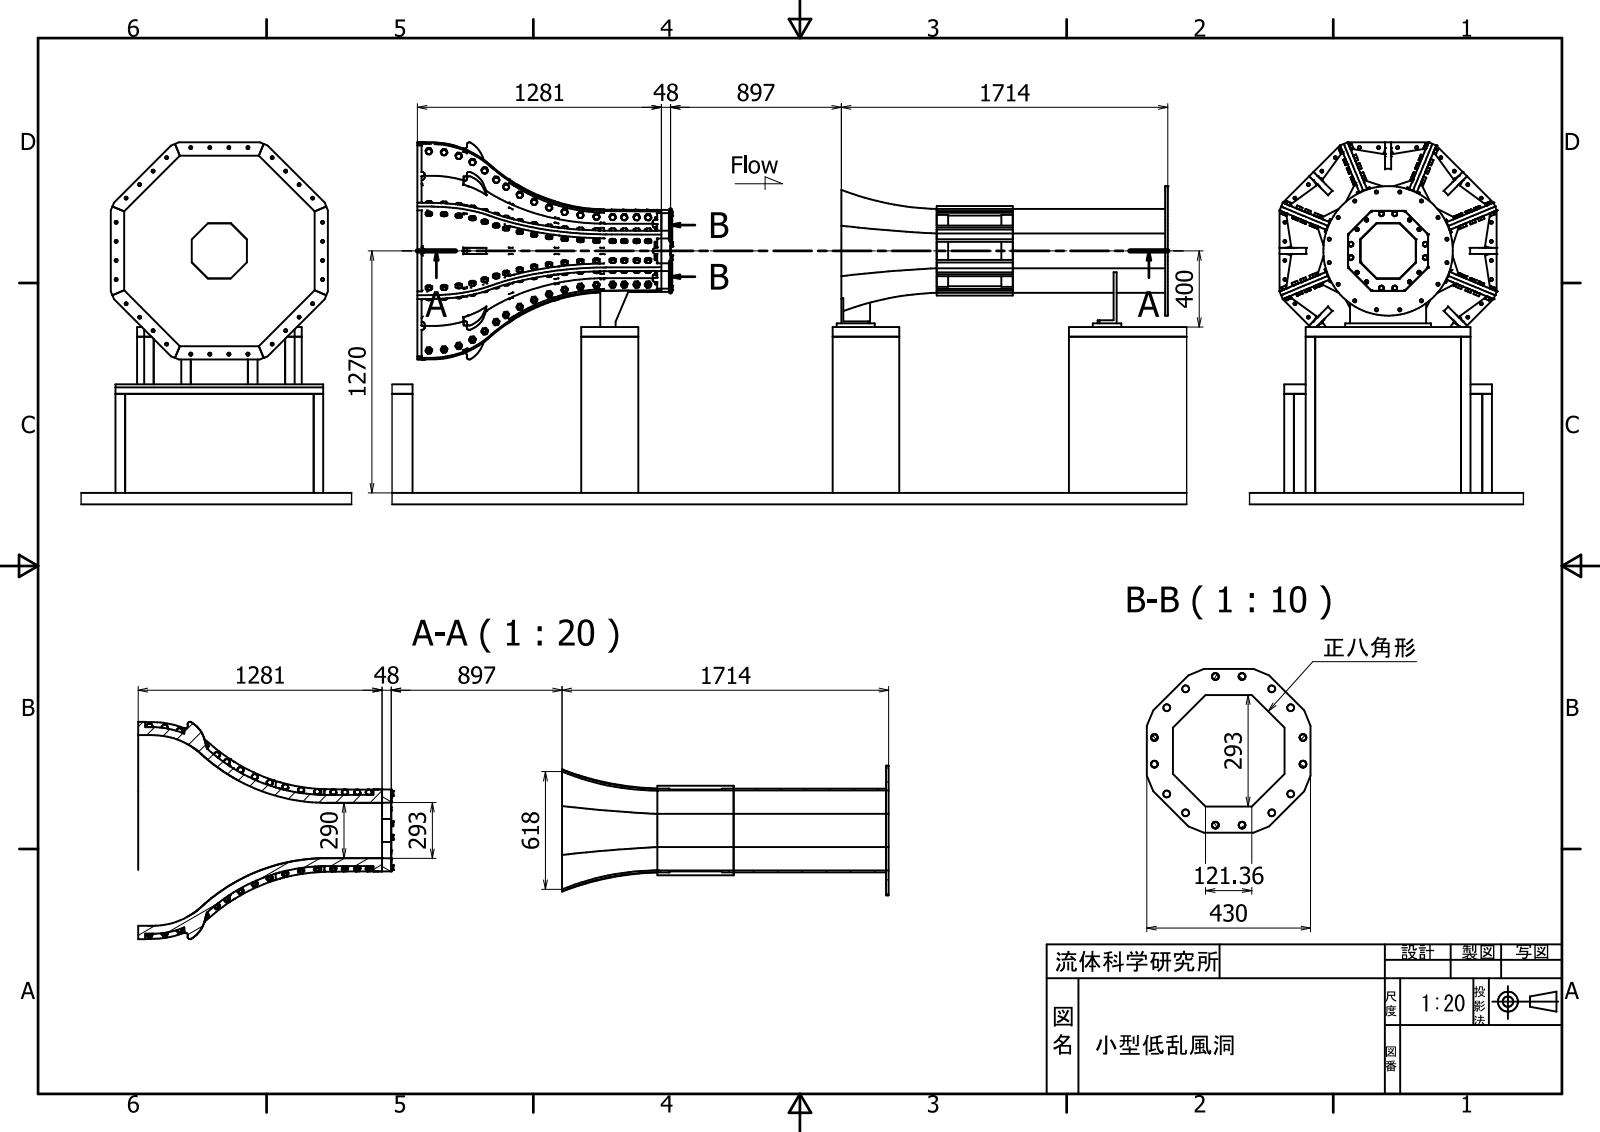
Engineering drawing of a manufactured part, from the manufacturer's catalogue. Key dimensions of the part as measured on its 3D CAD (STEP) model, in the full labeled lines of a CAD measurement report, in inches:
Part name (STEP PRODUCT): 小型低乱調風洞 (開放_コレクタ2 )_rev2; 測定部台座; 測定部台座A; 測定部台座A_01 (+8 more)
STEP written by: Autodesk Inventor 2023 (AUTOMOTIVE_DESIGN)
Units: inches
Bodies: 341 solids, 9617 faces (4120 planar, 1196 cylindrical, 4301 other)
Overall size (bounding box): 275.394 × 176.772 × 74.803
Volume: 157 500 in³ · Surface area: 169 700 in²
Round holes (diameter × count): ⌀0.748 ×150, ⌀0.689 ×136, ⌀0.787 ×136, ⌀0.63 ×48, ⌀0.591 ×44, ⌀0.262 ×42, ⌀0.709 ×16, ⌀0.281 ×4, ⌀0.551 ×4, ⌀0.571 ×4, ⌀0.425 ×2
Round bosses / shafts (diameter × count): ⌀1.181 ×136, ⌀0.787 ×136, ⌀0.945 ×16, ⌀0.63 ×8, ⌀26.772 ×1
Partial cylindrical surfaces — rounded edges, fillets, slot ends (radius × count): R0.276 ×153, R0.512 ×16, R0.63 ×12, R0.236 ×8, R5.906 ×8
Main face-to-face distances: 2.362, 1.969, 11.811, 13.78, 4.429, 36.516, 32.087, 35.039, 34.646, 32.283
Hole centre spacings: 3.346, 16.726, 7.48, 23.655, 10.579, 14.961, 3.15, 26.97
